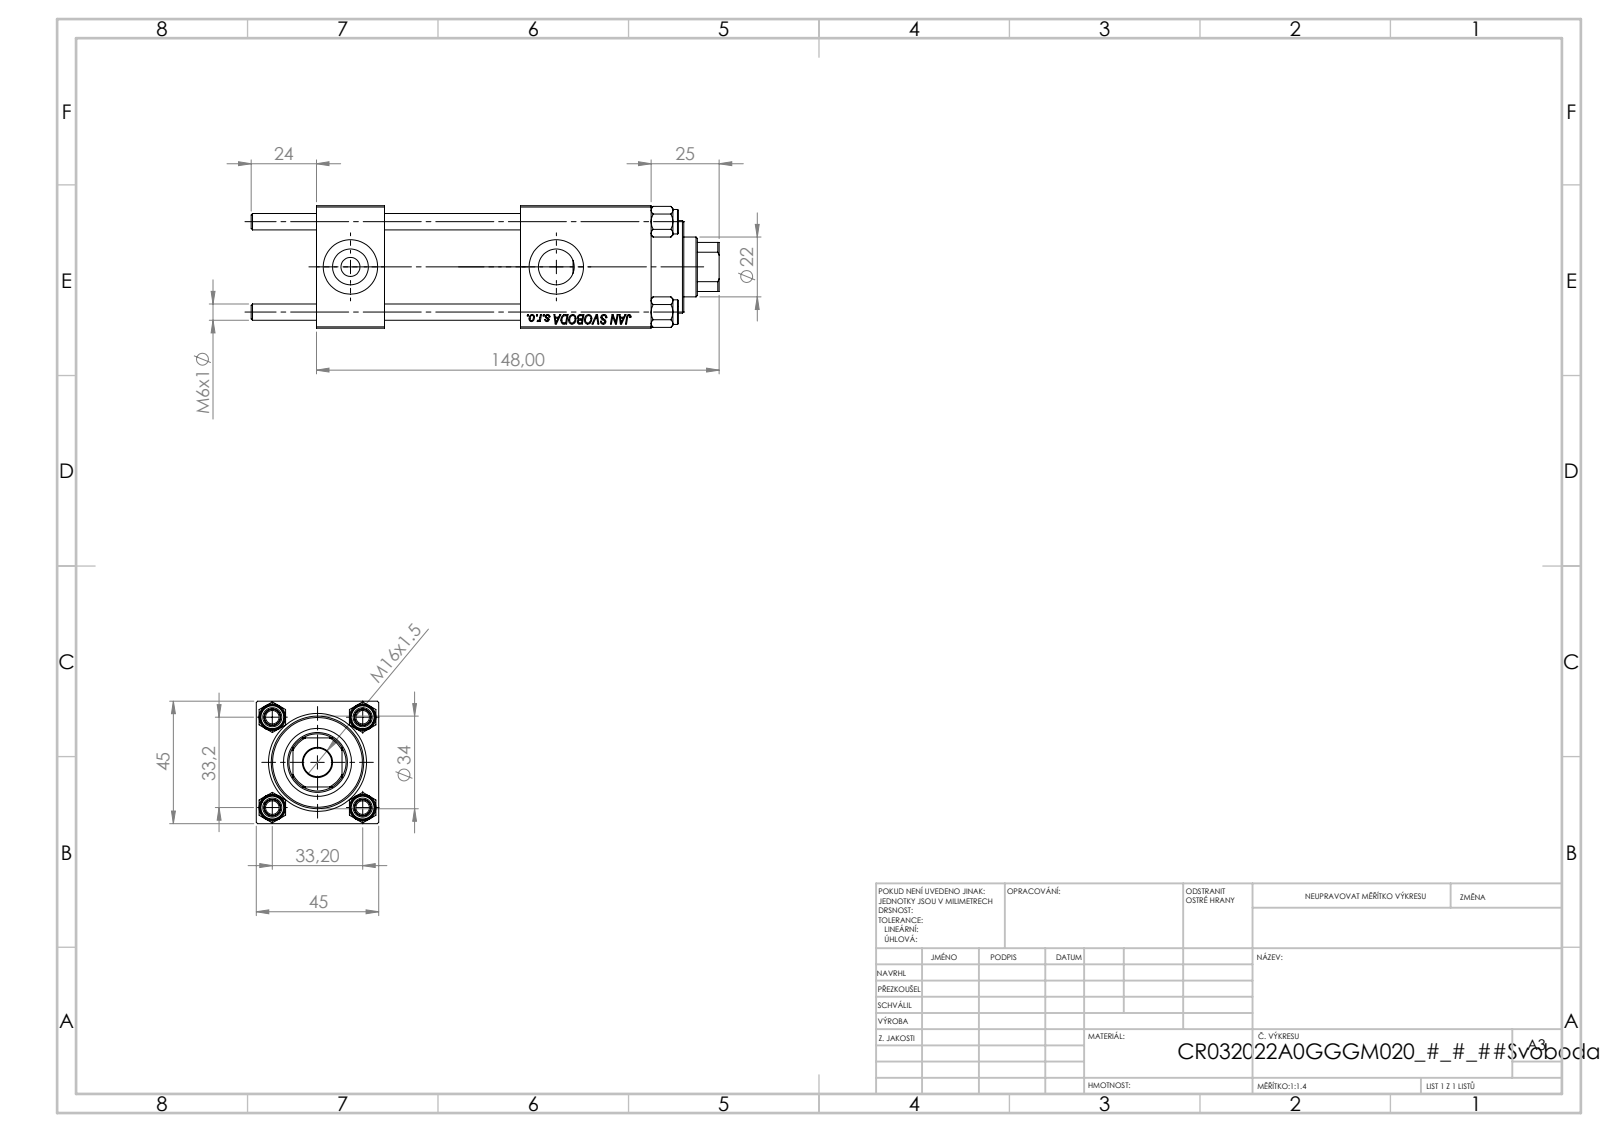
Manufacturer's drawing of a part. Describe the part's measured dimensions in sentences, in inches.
The part is named "V215CR_BODY_A; V215CR_VCP; CR025_012_A_0_G_A_G_M_020_+#_##_TYCINKA; V215_VC_A (+1 more)". Its 3-D file was written by "SolidWorks 2019 (CONFIG_CONTROL_DESIGN)". It is 11 solids with 1132 faces: 517 planar, 79 cylindrical and 536 other. Overall it measures 6.772 by 1.772 by 1.772 inches. Its volume is 13.07 cubic inches and its surface area 119.4 square inches. Round holes: 4 of diameter 0.236, 2 of diameter 0.276, 2 of diameter 0.518, 2 of diameter 0.787, 1 of diameter 0.413, 1 of diameter 0.866, 1 of diameter 0.945, 1 of diameter 0.984, 1 of diameter 1.26, 1 of diameter 1.299. Round bosses or shafts: 4 of diameter 0.354, 1 of diameter 1.496, 1 of diameter 1.339. Partial cylindrical surfaces (rounded edges, fillets, slot ends): 1 of radius 0.413. The main face-to-face distances are 1.772, 0.984, 4.843, 1.969, 2.953, 3.858, 1.89, 3.713, 2.728, 0.76. The hole center spacings are 0.924, 1.307, 1.848, 2.979.
